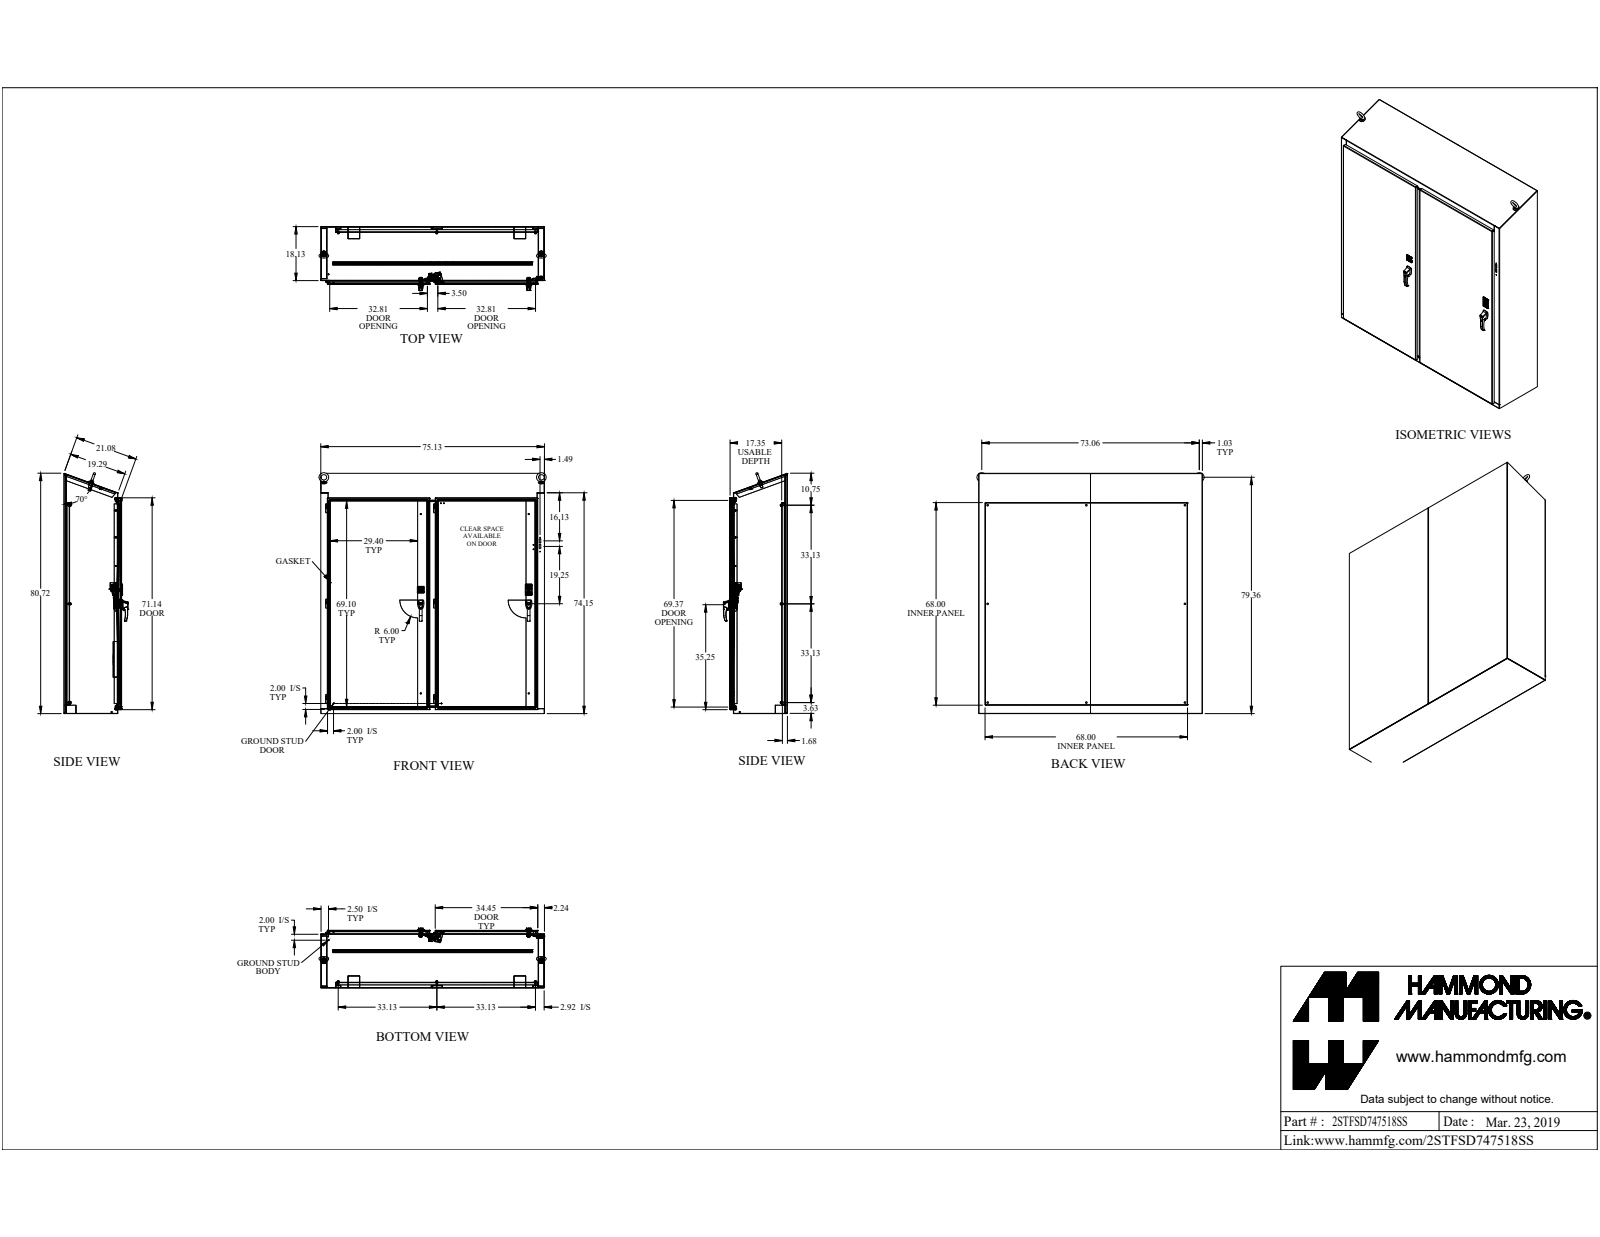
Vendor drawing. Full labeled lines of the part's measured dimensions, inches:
Part name (STEP PRODUCT): 2STFSD747518SS
STEP written by: SolidWorks 2019 (CONFIG_CONTROL_DESIGN)
Units: inches
Bodies: 210 solids, 3274 faces (1902 planar, 992 cylindrical, 380 other)
Overall size (bounding box): 80.884 × 76.307 × 21.491
Volume: 2 640 in³ · Surface area: 52 576 in²
Round holes (diameter × count): ⌀0.196 ×11, ⌀0.281 ×9, ⌀0.307 ×9, ⌀0.35 ×8, ⌀0.563 ×8, ⌀0.25 ×7, ⌀0.313 ×6, ⌀0.445 ×6, ⌀0.257 ×4, ⌀0.282 ×4, ⌀0.375 ×4, ⌀0.39 ×4
Round bosses / shafts (diameter × count): ⌀0.25 ×18, ⌀1 ×12, ⌀0.65 ×9, ⌀0.375 ×9, ⌀0.332 ×8, ⌀0.75 ×6, ⌀0.625 ×5, ⌀0.5 ×5
Partial cylindrical surfaces — rounded edges, fillets, slot ends (radius × count): R0.125 ×66, R0.048 ×36, R0.143 ×36, R0.5 ×34, R0.03 ×28, R0.06 ×27, R0.25 ×24, R0.01 ×20
Main face-to-face distances: 0.095, 0.095, 19.256, 0.125, 1.812, 1.907, 1.687, 1.782, 75.03, 0.024
Hole centre spacings: 73.059, 74.07, 66.25, 33.125, 33.125, 29.768, 32.246, 36.256
